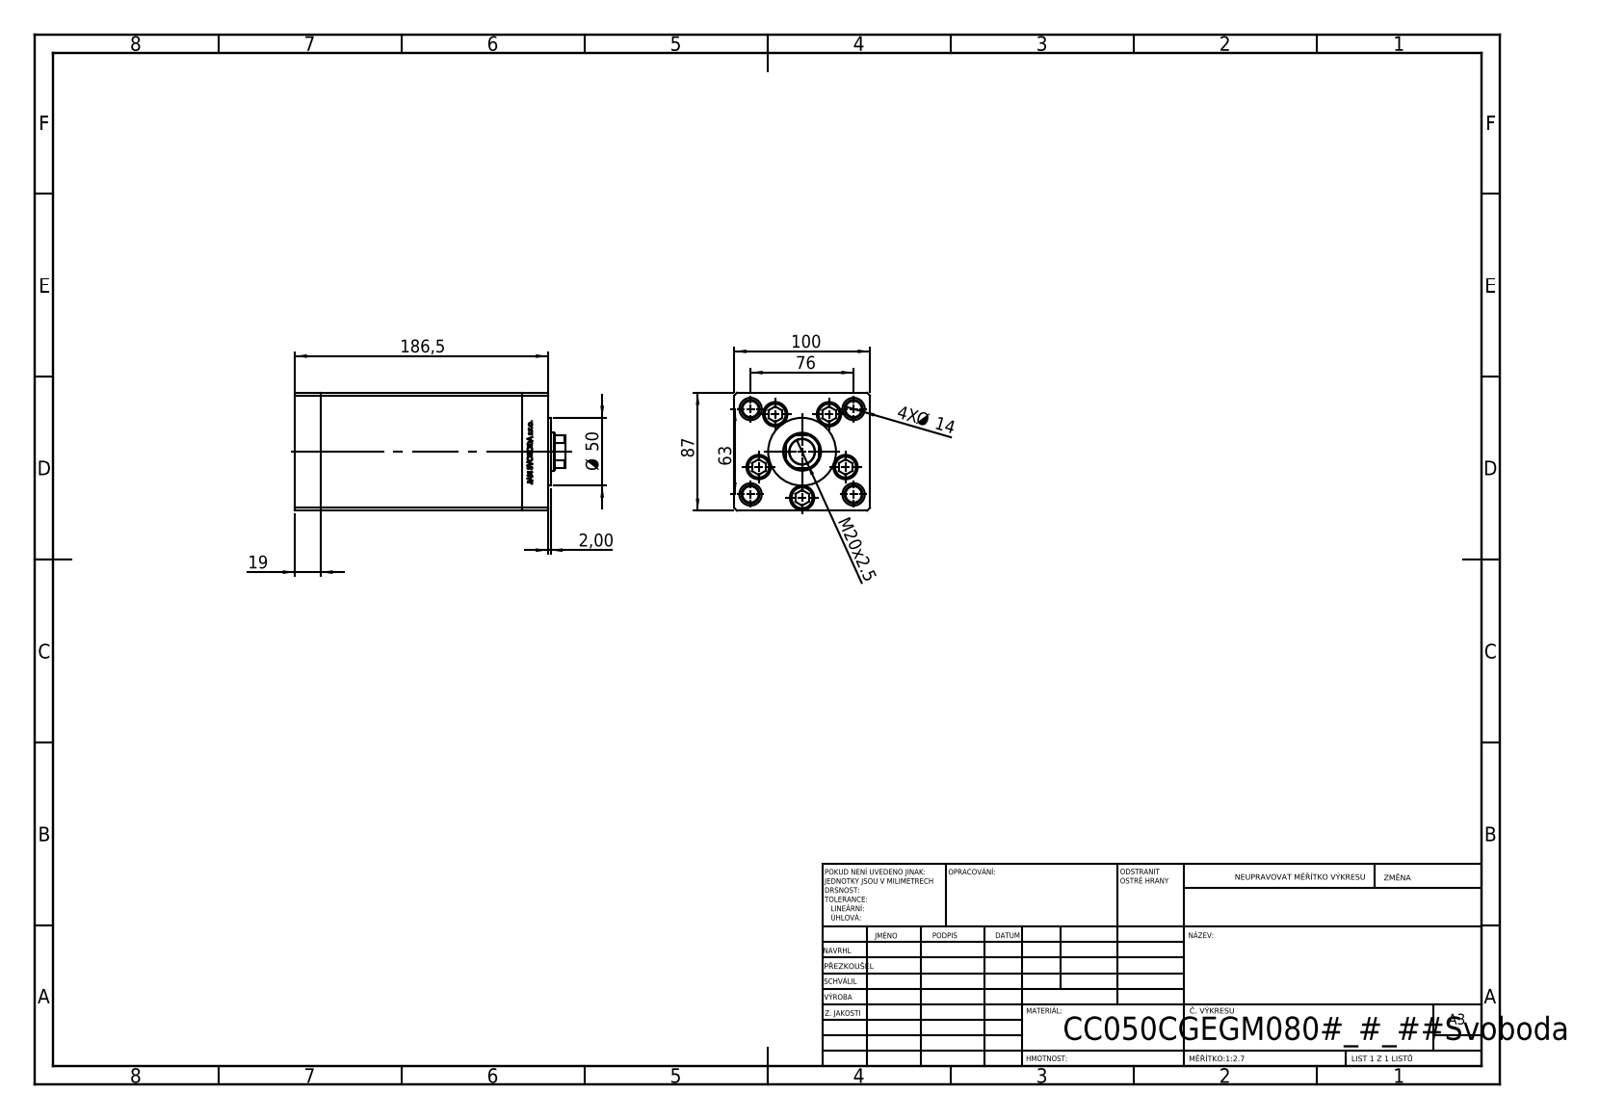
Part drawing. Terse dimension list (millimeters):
name: V220C_C MIDDLE; V220C BACK_C; V220C FRONT; ALLEN BOLT (+1 more)
written by: SolidWorks 2019 (CONFIG_CONTROL_DESIGN)
unit: mm
bodies: 13 solids, 1160 faces (538 planar, 160 cylindrical, 462 other)
size: 199.5 × 100 × 87
volume: 1 335 000 mm³; area: 228 555 mm²
holes: 9× ⌀13.5, 5× ⌀18, 4× ⌀12, 4× ⌀16.5, 1× ⌀17, 1× ⌀18.5, 1× ⌀28
bosses: 5× ⌀8, 4× ⌀17, 1× ⌀50
rounds: 2× R0.93, 1× R13.5
face distances: 100, 87, 19, 148.5, 167.5, 34.25, 186.5, 152.25, 133.25, 15.25
hole spacings: 34, 49.36, 18.59, 21.03, 38.08, 39.27, 40.83, 43.24
